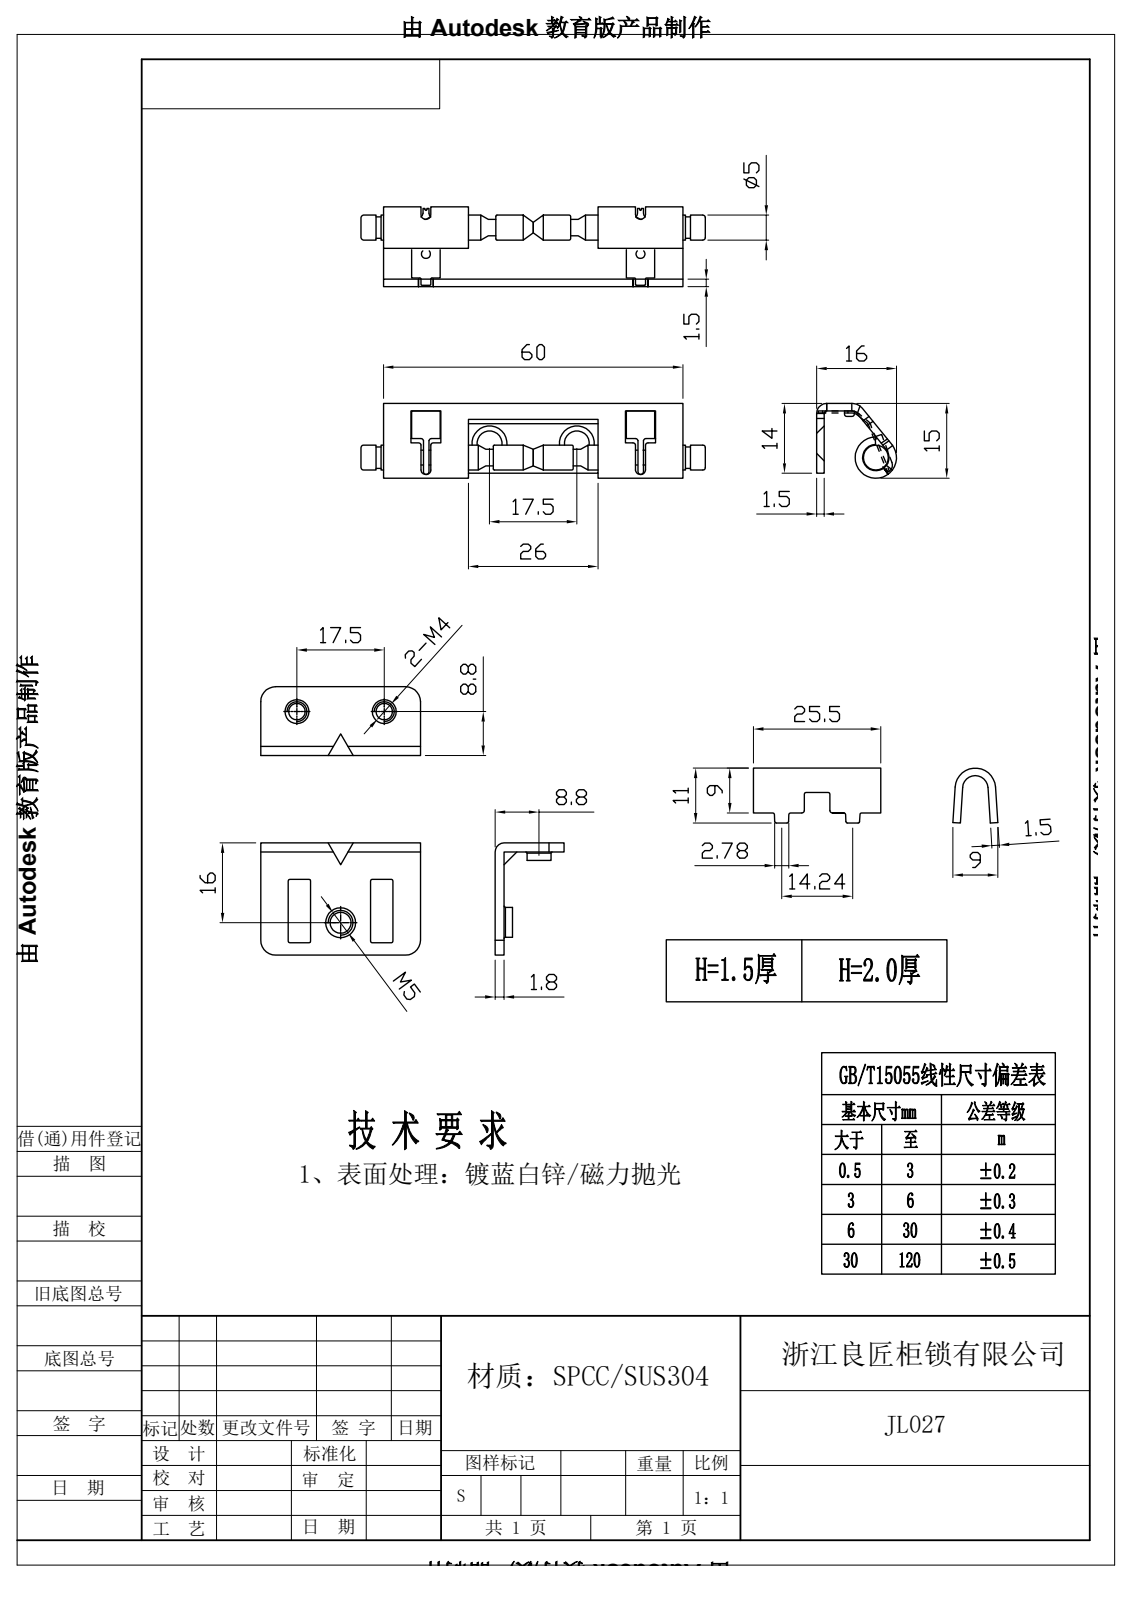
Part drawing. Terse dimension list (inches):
written by: Rhino 8.5 (CONFIG_CONTROL_DESIGN)
unit: in
bodies: 5 solids, 200 faces (93 planar, 77 cylindrical, 30 other)
size: 2.985 × 2.717 × 0.996
volume: 0.421 in³; area: 14.75 in²
holes: 2× ⌀0.13, 1× ⌀0.157, 1× ⌀0.209
bosses: 2× ⌀0.189, 1× ⌀0.327, 1× ⌀0.236, 1× ⌀0.197, 1× ⌀0.169, 1× ⌀0.13
rounds: 16× R0.012, 6× R0.118, 1× R0.02, 1× R0.039, 1× R0.071, 1× R0.079, 1× R0.098, 1× R0.1
face distances: 0.059, 0.071, 1.39, 1.331, 1.402, 1.461, 0.076, 0.064, 0.135, 0.217
hole spacings: 0.689
